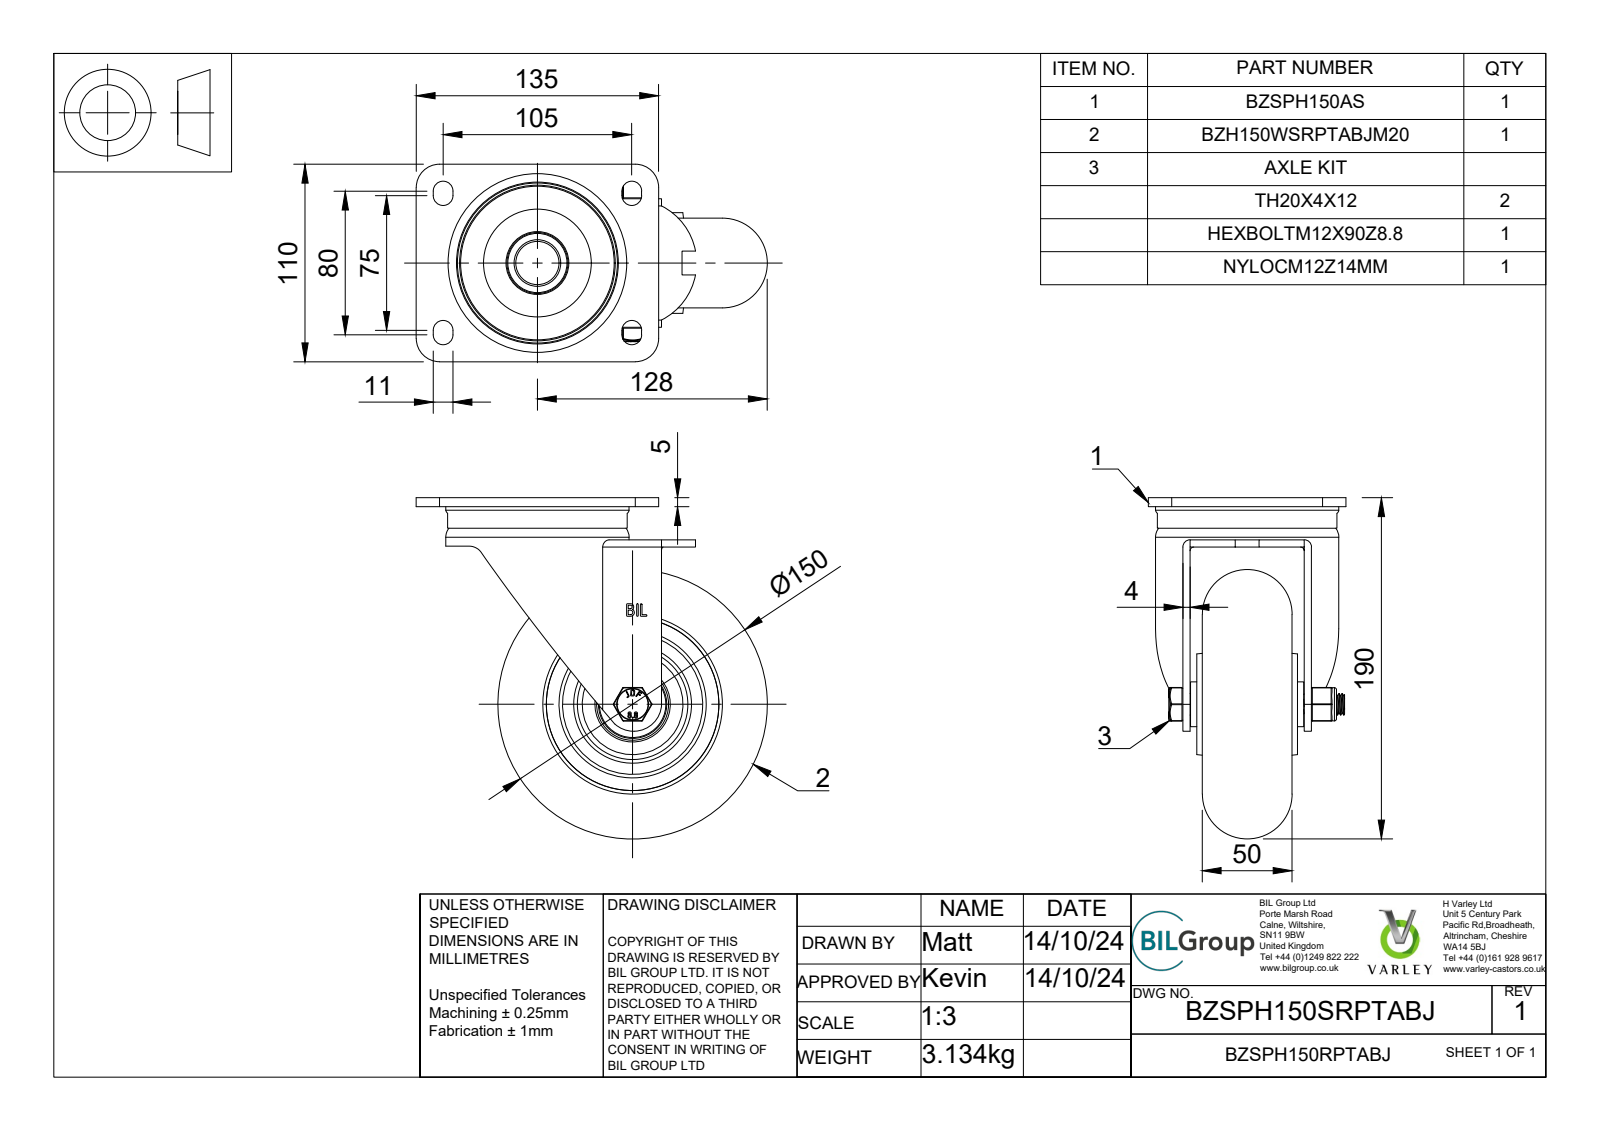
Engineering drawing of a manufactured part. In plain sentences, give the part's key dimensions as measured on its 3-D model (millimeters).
The part is named "BZSPH150SRPTABJ v3; BZSPH150AS - 2 v1; PRESSED STEEL TOP PLATE; PRESSED STEEL TOP PLATE Geometry (+6 more)". Its 3-D file was written by "Autodesk Translation Framework v13.20.0.188 (AUTOMOTIVE_DESIGN)". It is 157 solids with 1503 faces: 549 planar, 272 cylindrical and 682 other. Overall it measures 195.5 by 190 by 110 millimeters. Its volume is 864 738 cubic millimeters and its surface area 286 177 square millimeters. Round holes: 8 of diameter 8, 1 of diameter 12, 1 of diameter 12.2, 1 of diameter 14, 1 of diameter 20, 1 of diameter 20.4, 1 of diameter 26, 1 of diameter 35, 1 of diameter 36, 1 of diameter 38, 1 of diameter 42, 1 of diameter 71. Round bosses or shafts: 18 of diameter 8, 2 of diameter 24, 1 of diameter 102, 1 of diameter 100, 1 of diameter 74, 1 of diameter 72, 1 of diameter 37, 1 of diameter 36. Partial cylindrical surfaces (rounded edges, fillets, slot ends): 20 of radius 0.5, 8 of radius 5.5, 4 of radius 0.47, 4 of radius 0.9, 4 of radius 2, 4 of radius 13, 3 of radius 1, 2 of radius 0.89. The main face-to-face distances are 4, 9, 5, 6, 13, 18, 32.75, 38.75, 67.5, 28.75. The hole center spacings are 42.09, 55, 77.78, 101.63, 110.
